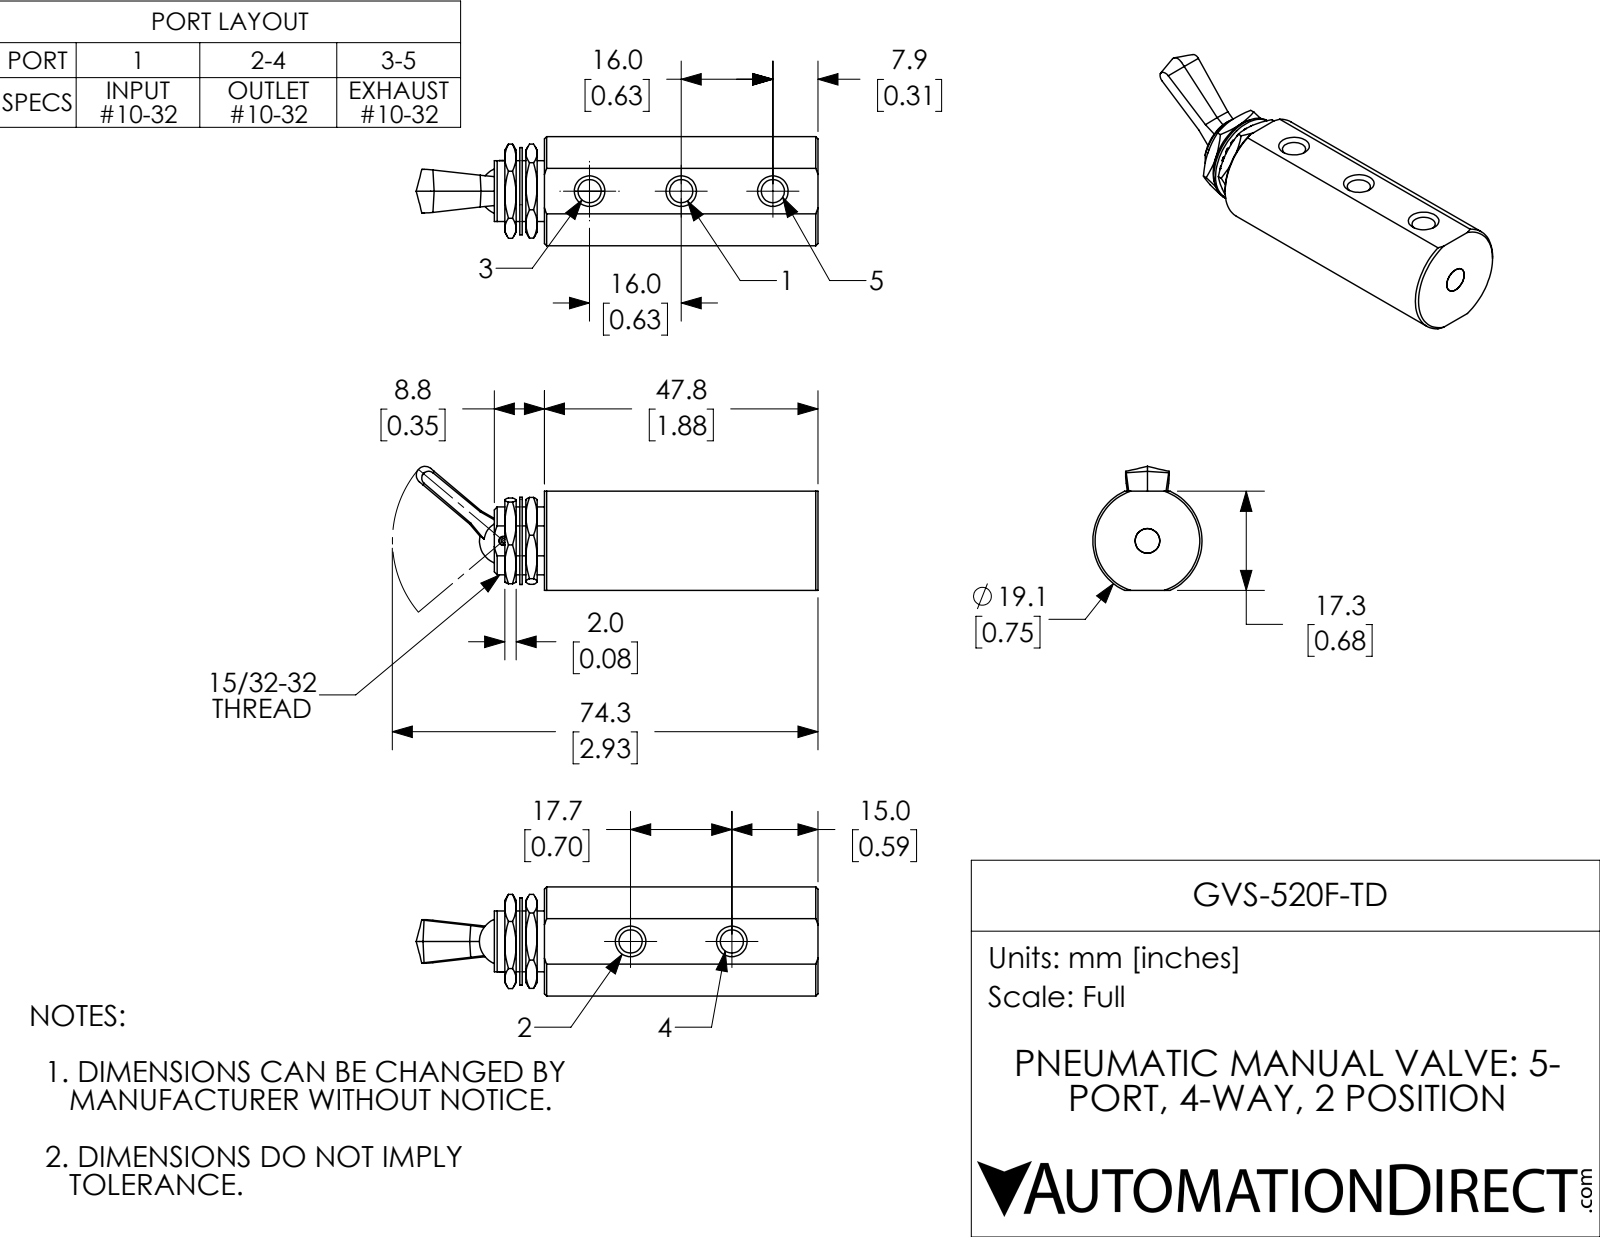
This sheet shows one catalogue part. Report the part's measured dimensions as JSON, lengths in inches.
{"part_name": "GVS-520F-TD", "step_written_by": "SolidWorks 2018 (AUTOMOTIVE_DESIGN)", "units": "inches", "bodies": {"solids": 7, "faces": 254, "planar": 96, "cylindrical": 94, "other": 64}, "overall_size": [2.762, 0.853, 0.75], "volume_in3": 0.687, "surface_area_in2": 10.72, "round_holes": [[0.159, 5], [0.03, 1], [0.063, 1], [0.07, 1], [0.169, 1], [0.29, 1], [0.332, 1], [0.415, 1], [0.438, 1]], "round_bosses_or_shafts": [[0.6, 1], [0.063, 1]], "partial_cylinders_radius": [[0.233, 1], [0.239, 1], [0.26, 1], [0.375, 1]], "face_to_face_distances": [0.682, 0.155, 1.725, 1.88, 0.12, 1.035, 0.145, 0.078, 0.067, 0.69], "hole_center_spacings": [0.282, 0.348, 0.63, 0.978, 0.696, 1.26]}
